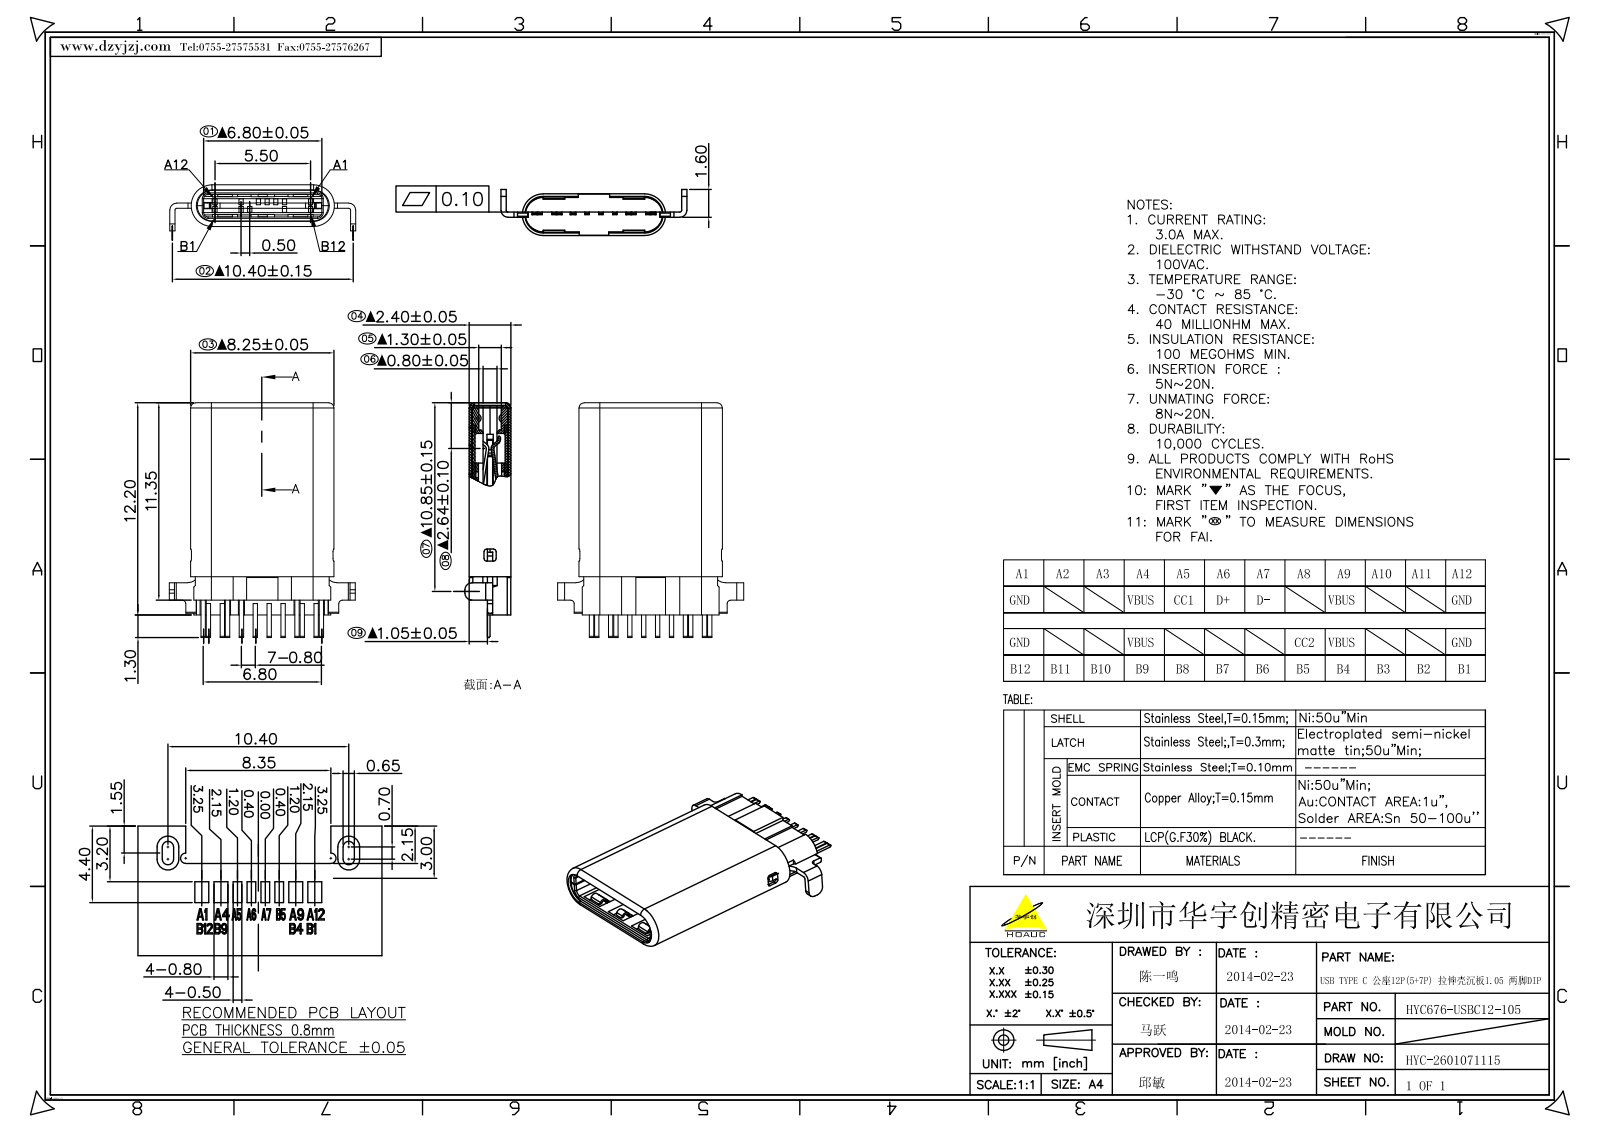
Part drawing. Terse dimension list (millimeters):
name: XDS-B_TC_2_M_107A_ASM
written by: CREO PARAMETRIC BY PTC INC, 2022073 (AUTOMOTIVE_DESIGN)
unit: mm
bodies: 1 solid, 447 faces (337 planar, 102 cylindrical, 8 other)
size: 13.5 × 10.7 × 2.65
volume: 180 mm³; area: 420 mm²
rounds: 12× R0.15, 8× R0.3, 6× R0.25, 4× R0.1, 4× R0.4, 4× R1.03, 2× R0.11, 2× R0.13
face distances: 0.8, 2.4, 1.6, 1.05, 0.55, 1.35, 1.04, 1.85, 0.5, 0.31
